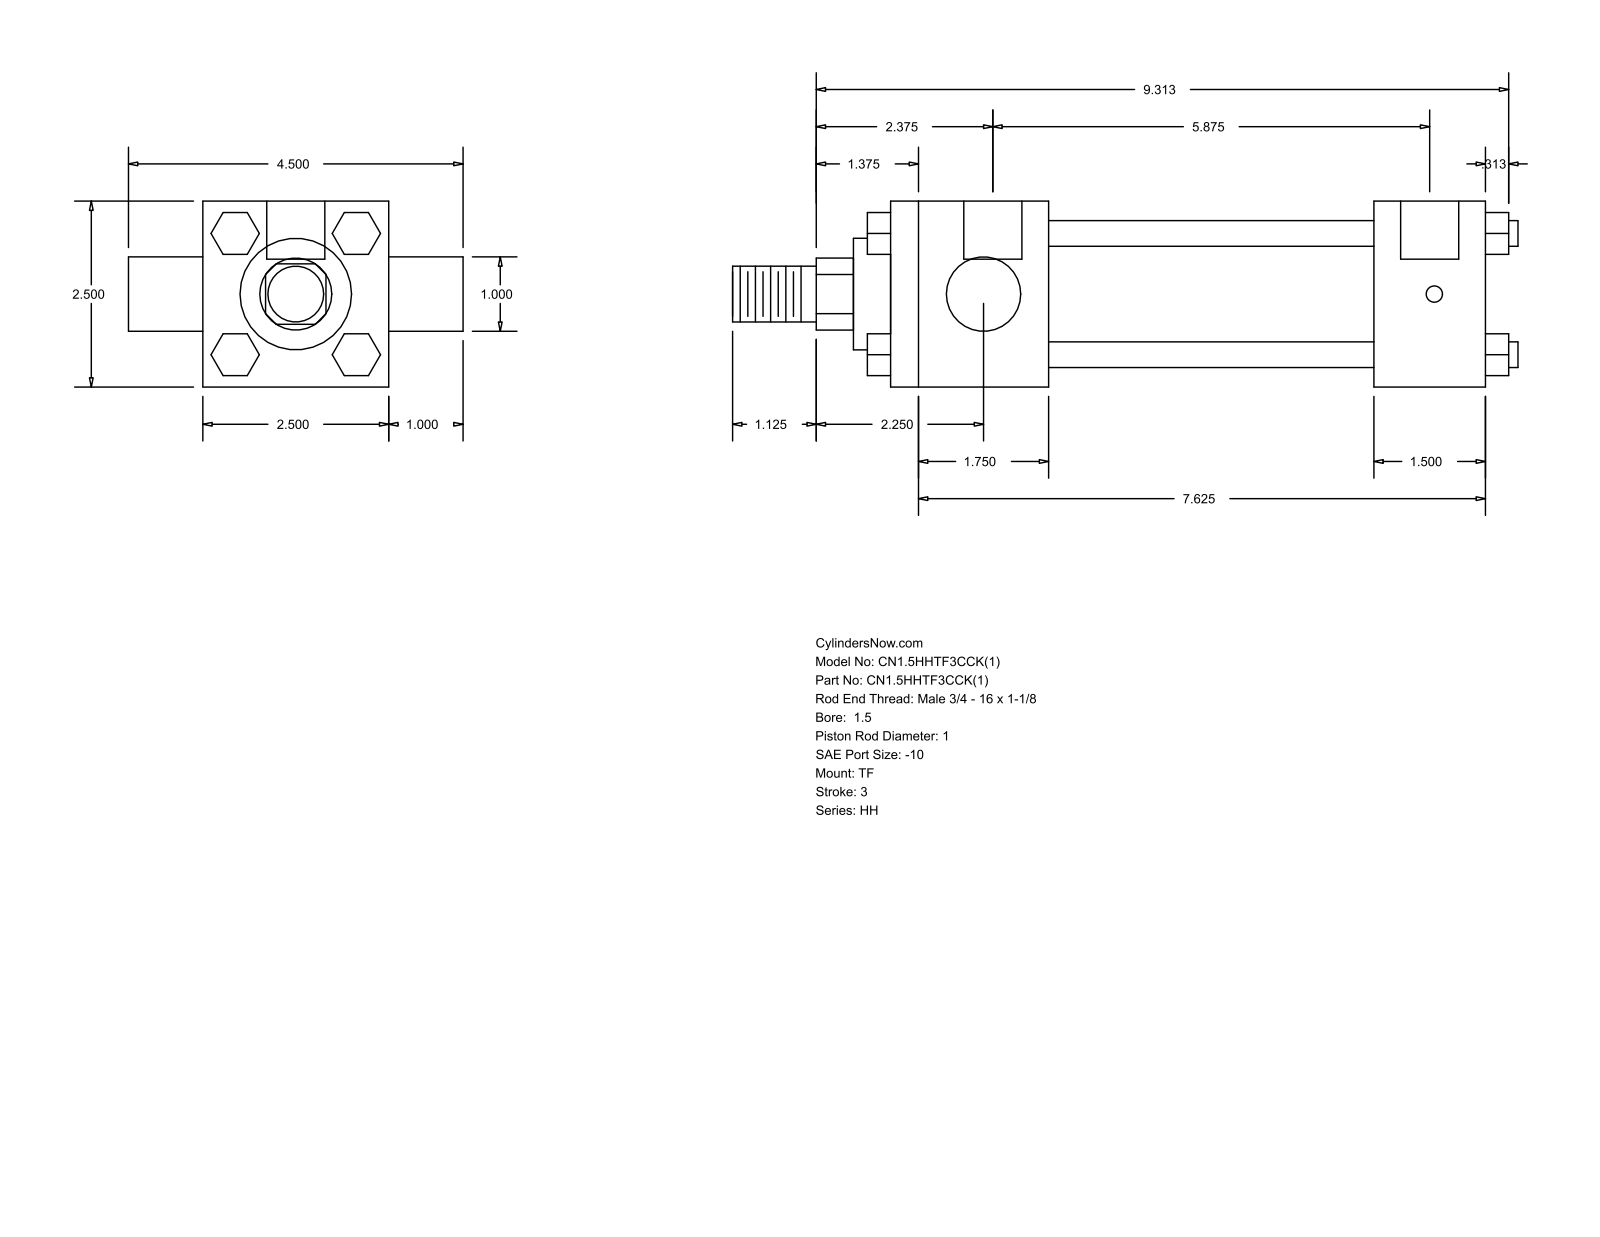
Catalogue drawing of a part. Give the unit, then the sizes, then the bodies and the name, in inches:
Units: inches
Overall size (bounding box): 10.563 × 4.5 × 2.5
Round holes (diameter × count): ⌀0.219 ×3, ⌀0.781 ×2
Round bosses / shafts (diameter × count): ⌀0.345 ×4, ⌀1 ×2, ⌀1.75 ×1, ⌀1.5 ×1, ⌀0.75 ×1
Partial cylindrical surfaces — rounded edges, fillets, slot ends (radius × count): R0.484 ×1
Main face-to-face distances: 2.5, 1.5, 5.875, 4.375, 2.125, 6.5, 8, 1, 0.815, 0.563
Hole centre spacings: 0.063, 5.937, 5.875, 6
Bodies: 0 solids, 120 faces (92 planar, 28 cylindrical, 0 other)
Part name (STEP PRODUCT): HH_TF__0150_1
STEP written by: GSSL Pune (CONFIG_CONTROL_DESIGN)
